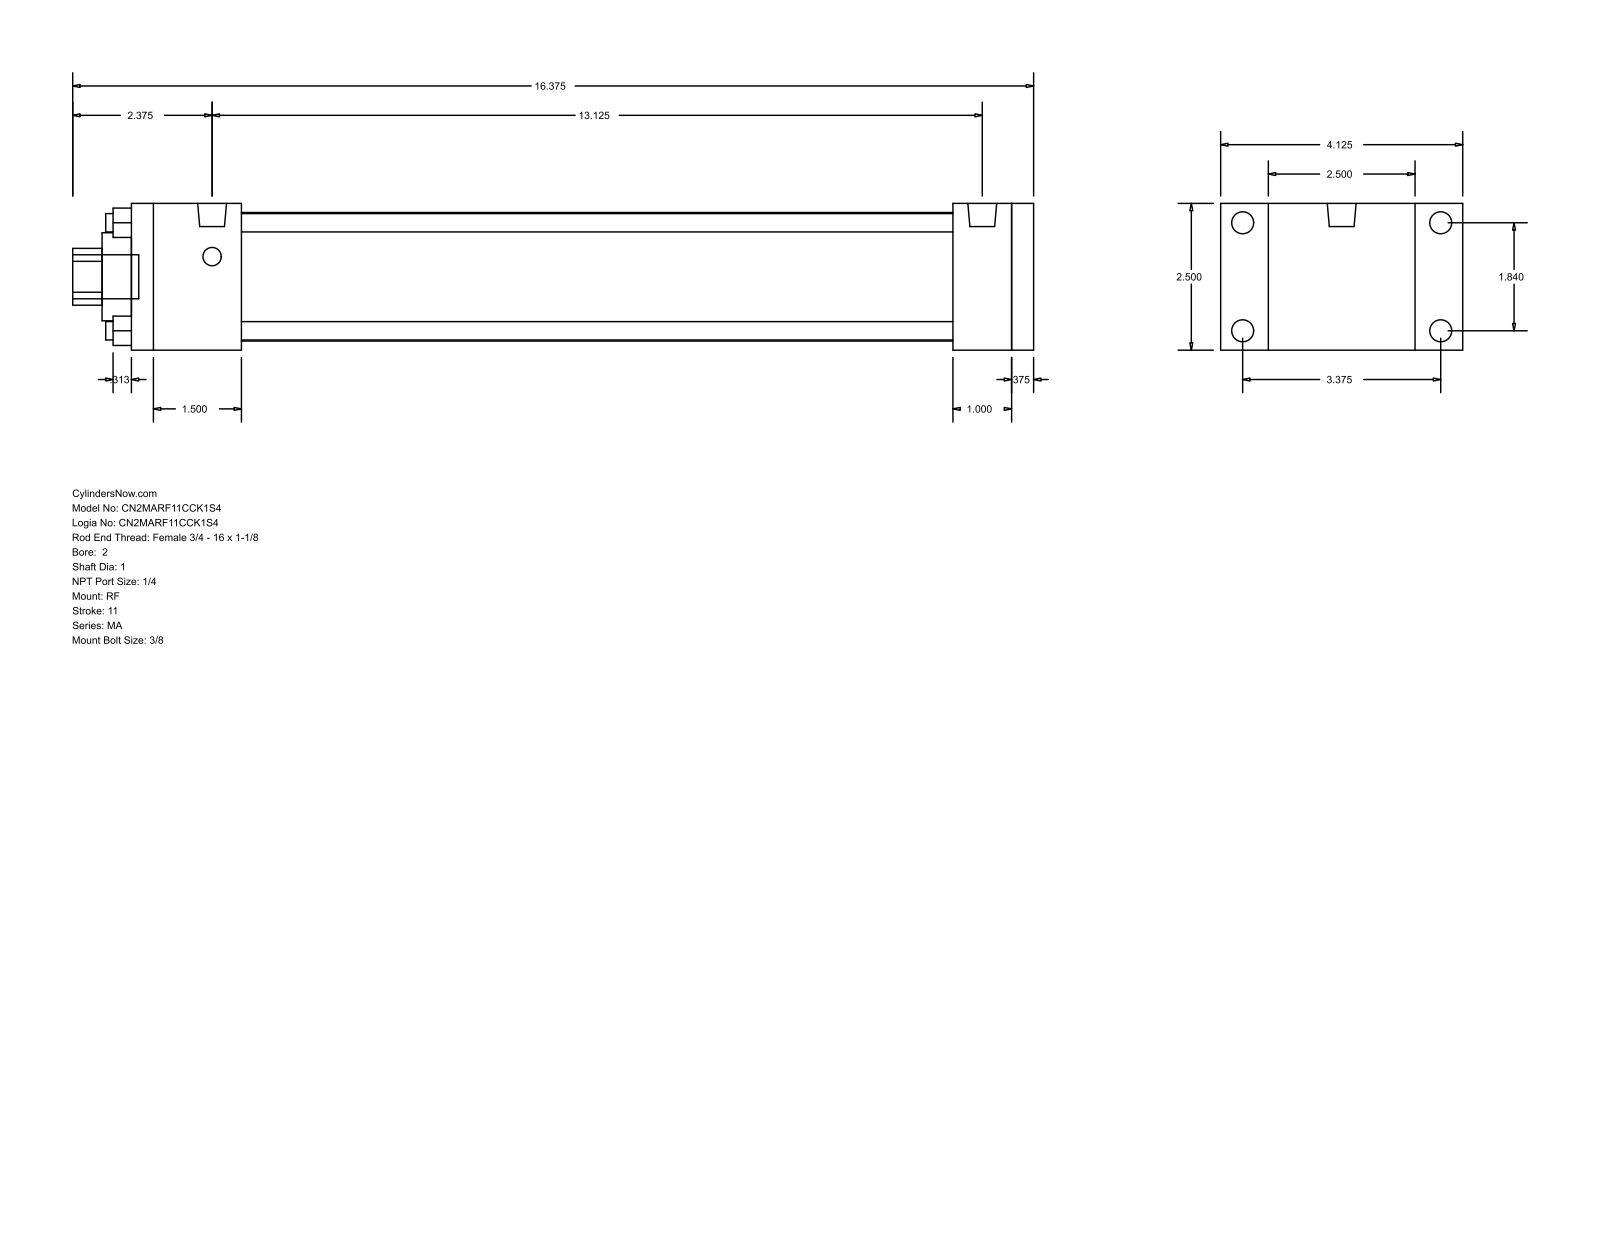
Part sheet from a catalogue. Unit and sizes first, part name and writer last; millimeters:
Units: millimetres
Overall size (bounding box): 415.93 × 104.78 × 63.5
Round holes (diameter × count): ⌀7.94 ×4, ⌀25.4 ×1, ⌀38.1 ×1, ⌀55.63 ×1
Round bosses / shafts (diameter × count): ⌀9.53 ×4, ⌀7.94 ×4, ⌀12.49 ×2, ⌀19.05 ×1
Partial cylindrical surfaces — rounded edges, fillets, slot ends (radius × count): R12.29 ×1
Main face-to-face distances: 63.5, 381, 9.53, 390.53, 25.4, 20.64, 12.7, 47.63, 333.37, 342.9
Hole centre spacings: 33.05, 46.74, 66.1
Bodies: 0 solids, 92 faces (64 planar, 28 cylindrical, 0 other)
Part name (STEP PRODUCT): MA_RF__0200_1
STEP written by: GSSL Pune (CONFIG_CONTROL_DESIGN)
